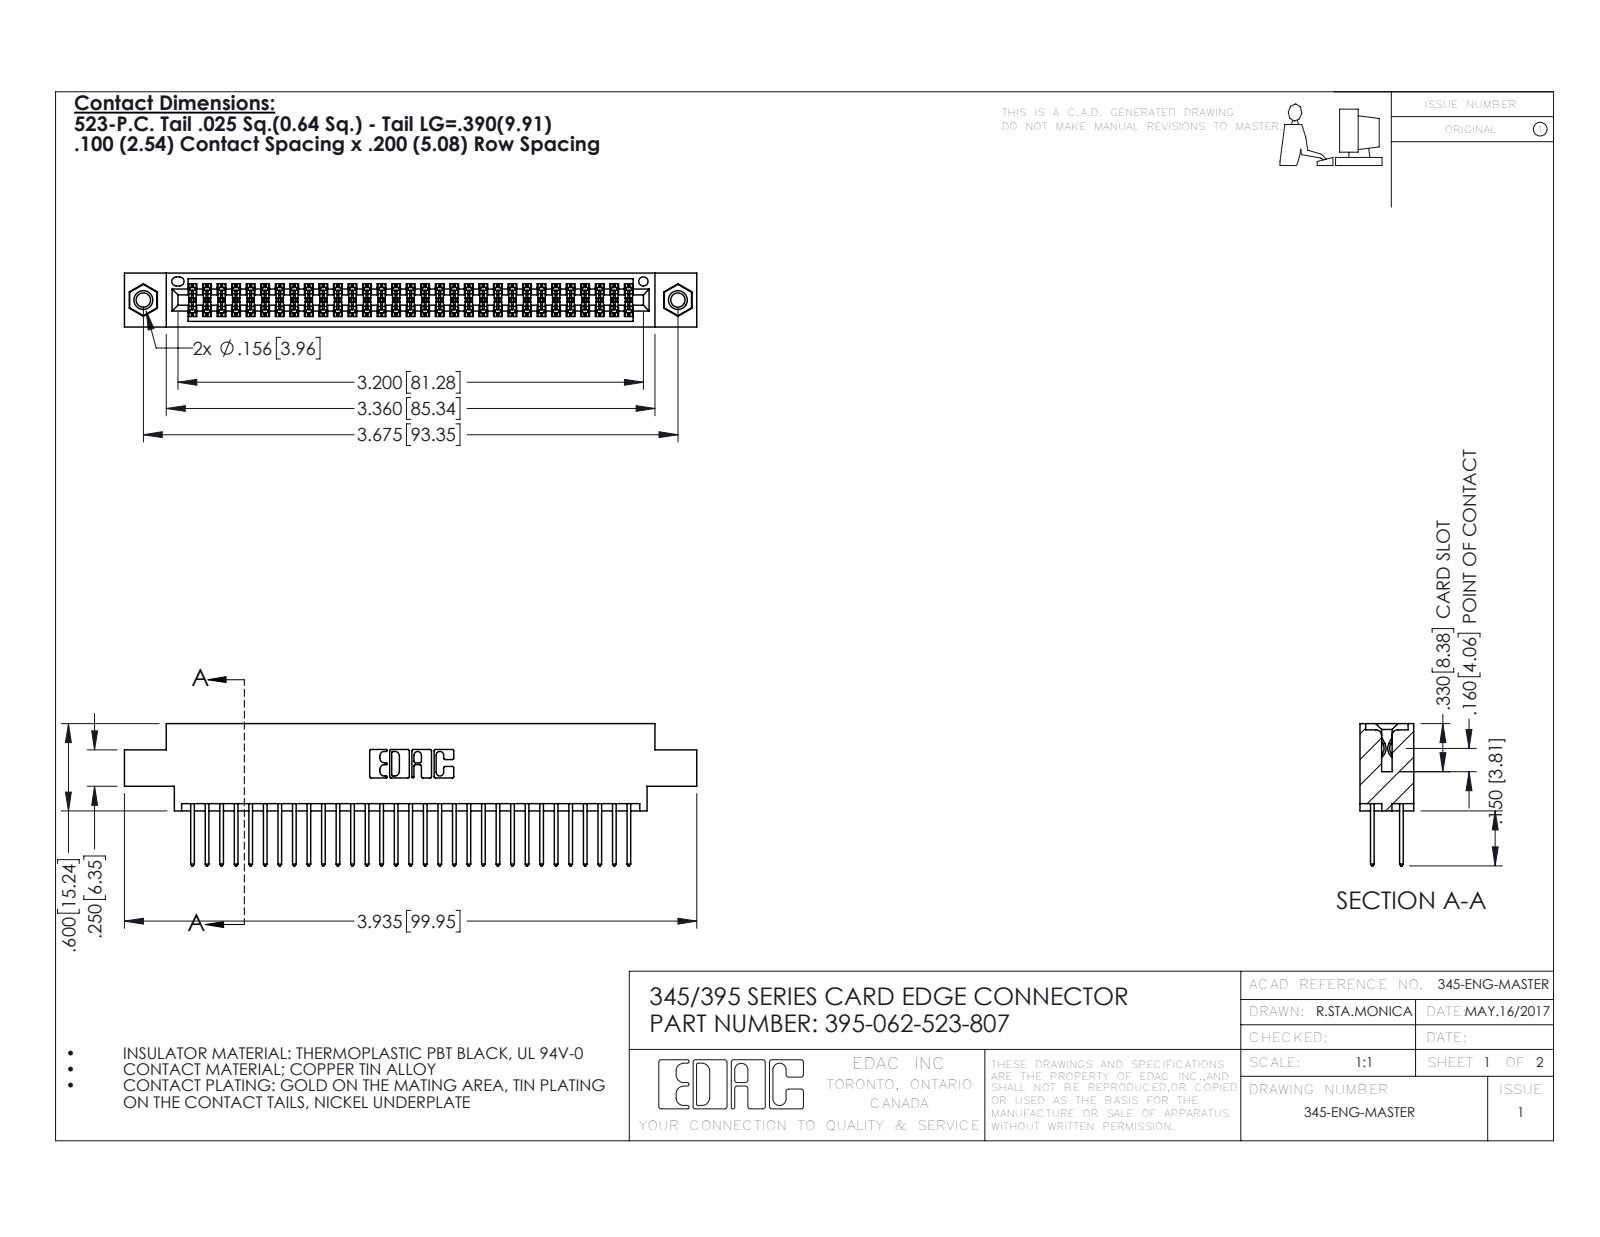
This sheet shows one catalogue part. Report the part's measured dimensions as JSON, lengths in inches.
{"part_name": "345-250-001_345-250-005-103; 395-062-523-807; 345 Part_0.170 Offset - 0.156 Dia-TI; 345-292-001_345-293-123", "step_written_by": "SolidWorks 2016 (CONFIG_CONTROL_DESIGN)", "units": "inches", "bodies": {"solids": 65, "faces": 3290, "planar": 2162, "cylindrical": 1112, "other": 16}, "overall_size": [3.935, 0.977, 0.37], "volume_in3": 0.586, "surface_area_in2": 22.83, "round_holes": [[0.098, 2], [0.125, 2], [0.156, 2], [0.064, 1]], "round_bosses_or_shafts": [[0.155, 2]], "partial_cylinders_radius": [[0.006, 93], [0.01, 62], [0.01, 22], [0.007, 6], [0.031, 6], [0.026, 3], [0.014, 2], [0.019, 2]], "face_to_face_distances": [0.072, 0.298, 0.2, 0.098, 0.272, 0.025, 0.37, 0.225, 0.175, 0.149], "hole_center_spacings": [0.27, 3.44, 3.675]}
